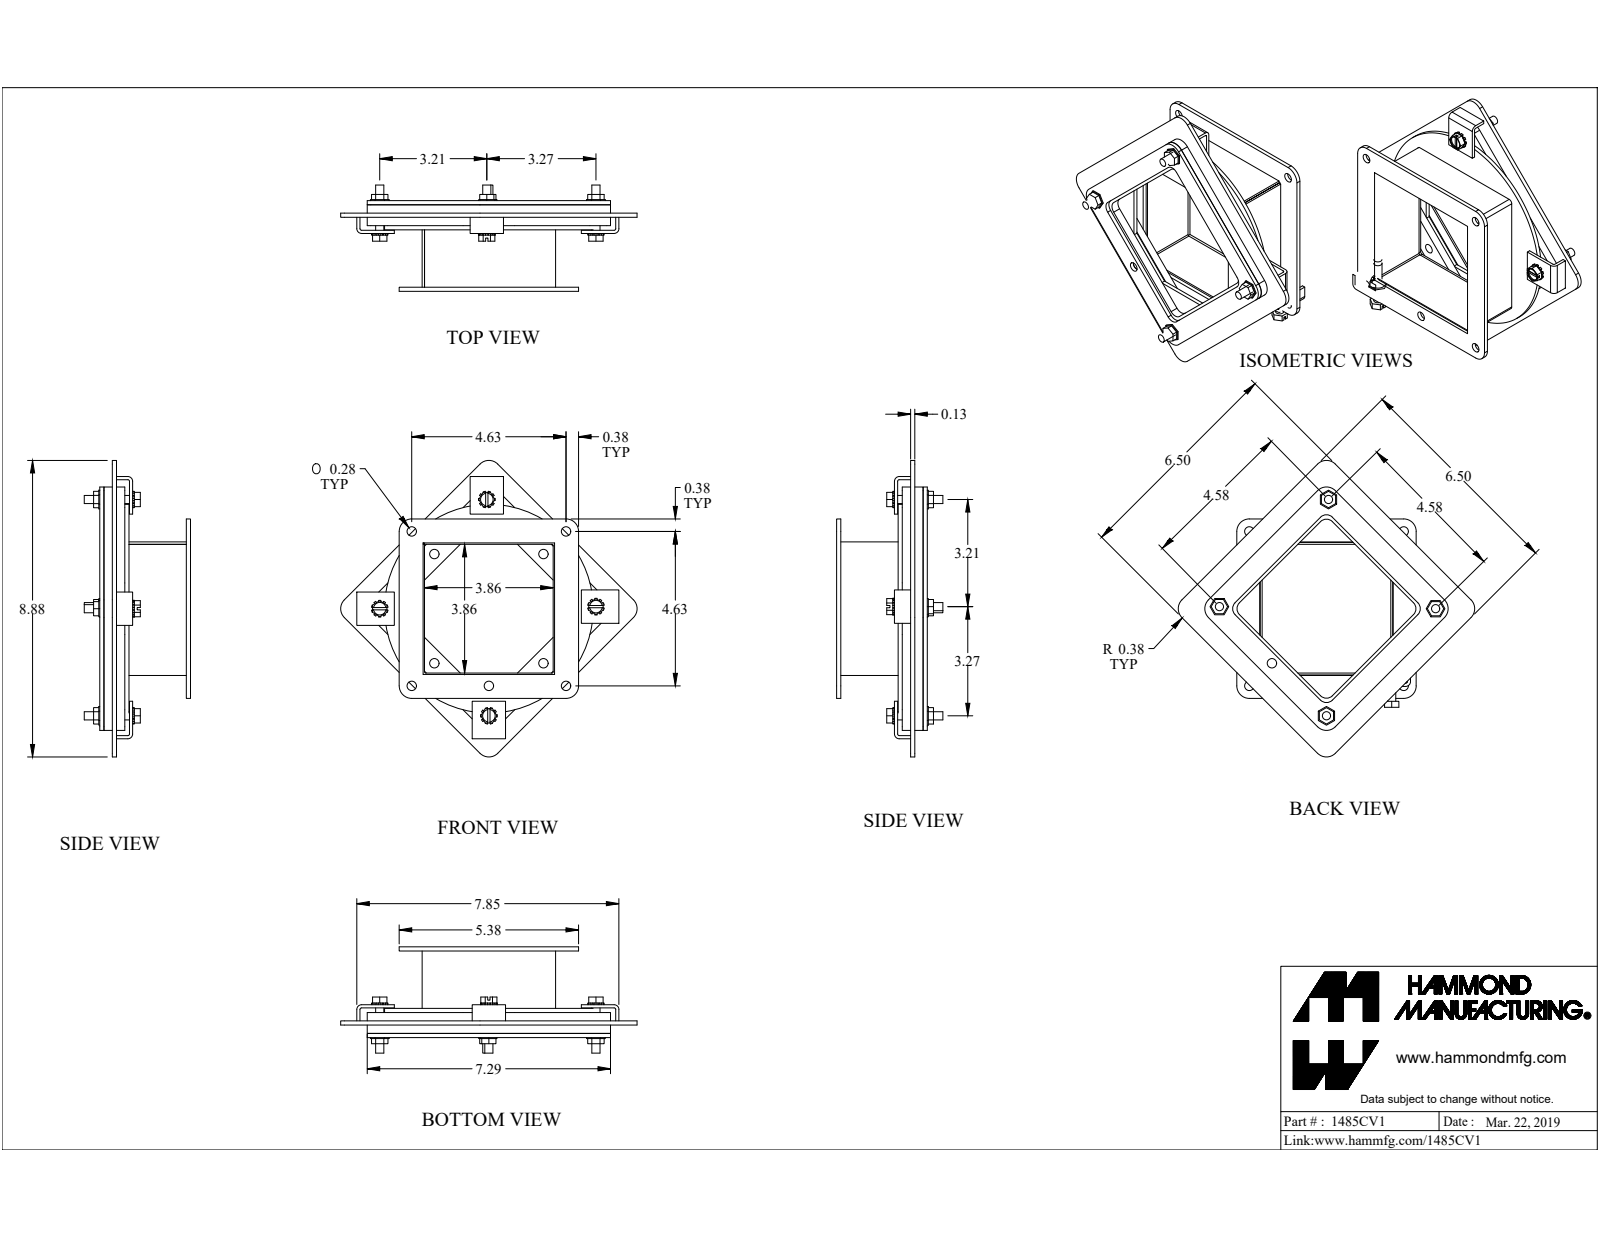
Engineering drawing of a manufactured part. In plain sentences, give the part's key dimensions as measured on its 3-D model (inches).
The part is named "1485CV1". Its 3-D file was written by "SolidWorks 2019 (CONFIG_CONTROL_DESIGN)". It is 34 solids with 667 faces: 463 planar, 191 cylindrical and 13 other. Overall it measures 8.882 by 8.882 by 3.434 inches. Its volume is 22.52 cubic inches and its surface area 378.1 square inches. Round holes: 16 of diameter 0.281, 6 of diameter 0.375, 5 of diameter 0.196, 4 of diameter 0.258, 4 of diameter 0.312, 2 of diameter 0.187, 2 of diameter 0.265, 2 of diameter 0.313, 1 of diameter 0.224. Round bosses or shafts: 5 of diameter 0.244, 2 of diameter 0.563, 2 of diameter 0.25, 1 of diameter 6.25. Partial cylindrical surfaces (rounded edges, fillets, slot ends): 16 of radius 0.25, 12 of radius 0.375, 9 of radius 0.048, 9 of radius 0.143, 4 of radius 0.062, 3 of radius 0.036, 3 of radius 0.108, 1 of radius 0.06. The main face-to-face distances are 0.25, 0.375, 2.593, 0.125, 0.125, 0.375, 2.218, 1.843, 0.5, 0.75. The hole center spacings are 2.313, 4.625, 5.171, 5.171, 4.006, 0.958, 2.503, 3.27.
